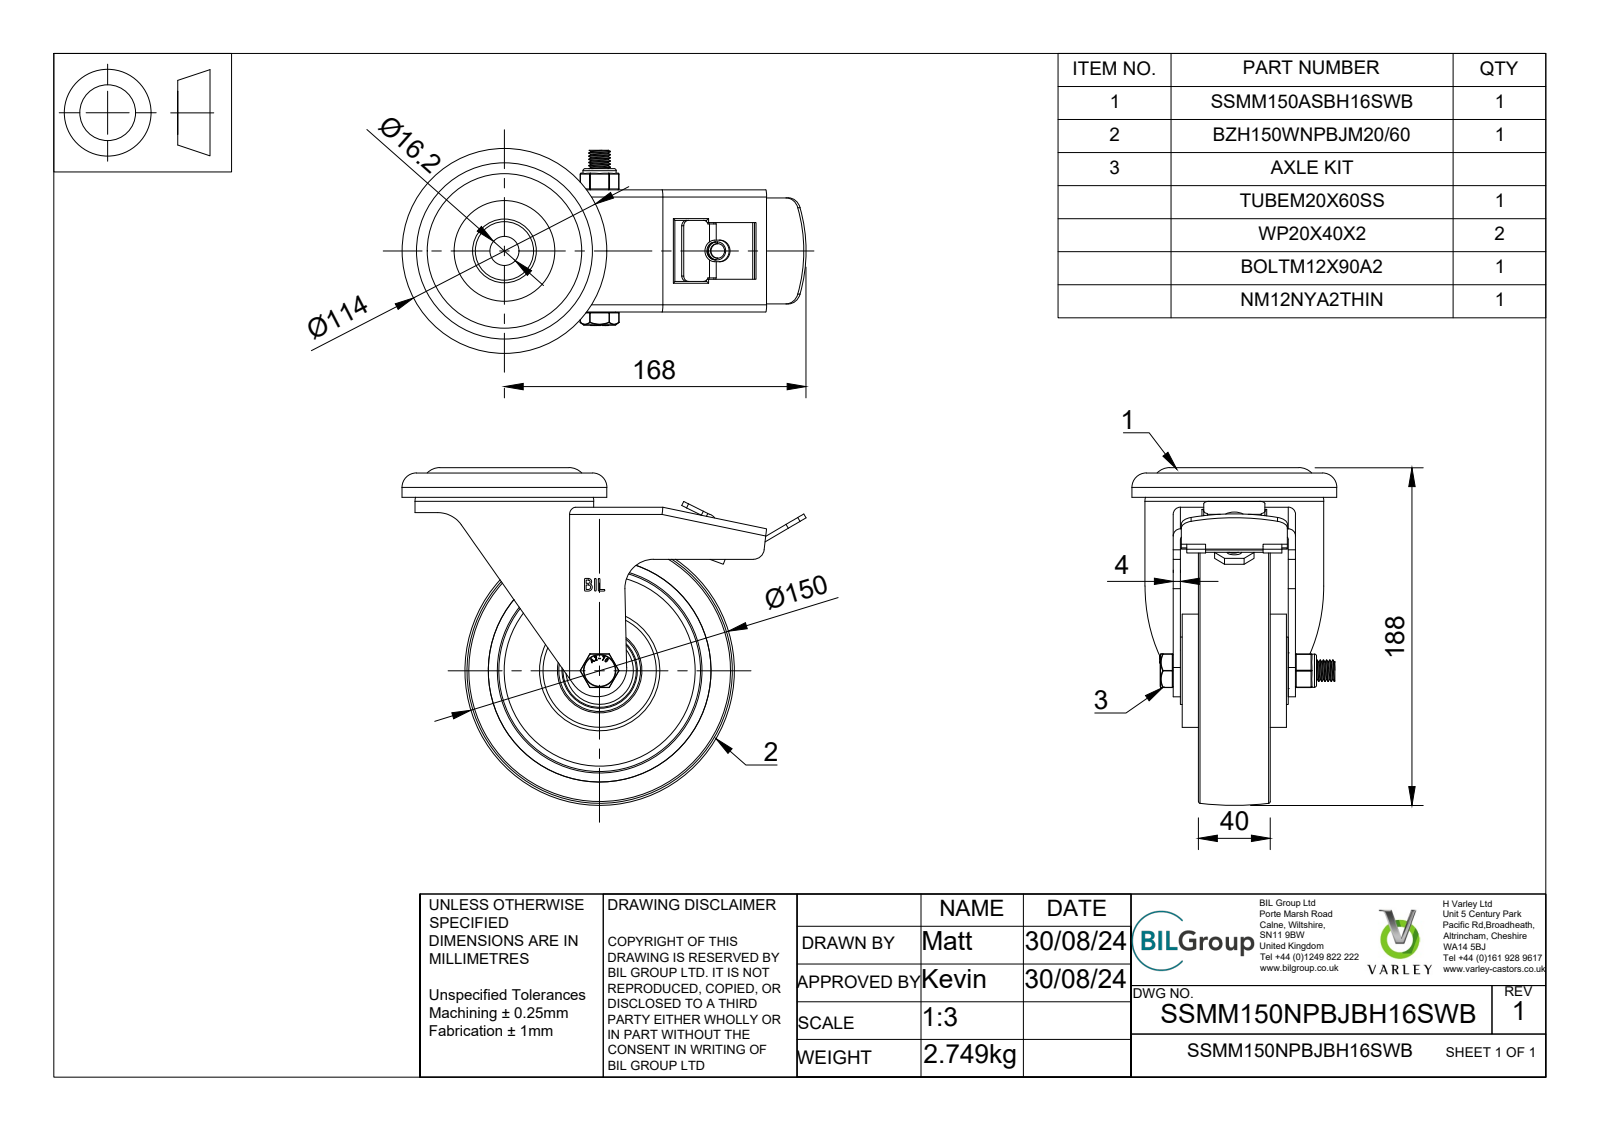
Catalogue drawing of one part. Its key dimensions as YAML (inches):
part_name: "SSMM150NPBJBH16SWB v4; SSMM150ASBH16SWB v1; STAINLESS STEEL HEAD; STAINLESS STEEL FORKS (+8 more)"
step_written_by: "Autodesk Translation Framework v13.14.0.145 (AUTOMOTIVE_DESIGN)"
units: inches
bodies: {solids: 41, faces: 1266, planar: 543, cylindrical: 248, other: 475}
overall_size: [8.858, 7.402, 4.488]
volume: 44.25
surface_area: 448.9
round_holes:
  - {diameter: 0.394, count: 1}
  - {diameter: 0.404, count: 1}
  - {diameter: 0.472, count: 1}
  - {diameter: 0.48, count: 1}
  - {diameter: 0.492, count: 1}
  - {diameter: 0.551, count: 1}
  - {diameter: 0.638, count: 1}
  - {diameter: 0.787, count: 1}
  - {diameter: 0.827, count: 1}
  - {diameter: 1.122, count: 1}
  - {diameter: 1.213, count: 1}
  - {diameter: 1.587, count: 1}
round_bosses_or_shafts:
  - {diameter: 4.488, count: 1}
  - {diameter: 3.917, count: 1}
  - {diameter: 2.913, count: 1}
  - {diameter: 2.48, count: 1}
  - {diameter: 1.85, count: 1}
  - {diameter: 1.606, count: 1}
  - {diameter: 1.476, count: 1}
  - {diameter: 1.28, count: 1}
partial_cylinders:
  - {radius: 0.02, count: 22}
  - {radius: 0.01, count: 12}
  - {radius: 0.079, count: 8}
  - {radius: 0.039, count: 6}
  - {radius: 0.118, count: 4}
  - {radius: 0.157, count: 4}
  - {radius: 0.236, count: 3}
  - {radius: 0.315, count: 3}
face_to_face_distances: [0.039, 0.915, 0.394, 0.659, 1.969, 1.053, 1.309, 0.157, 0.551, 1.575]
